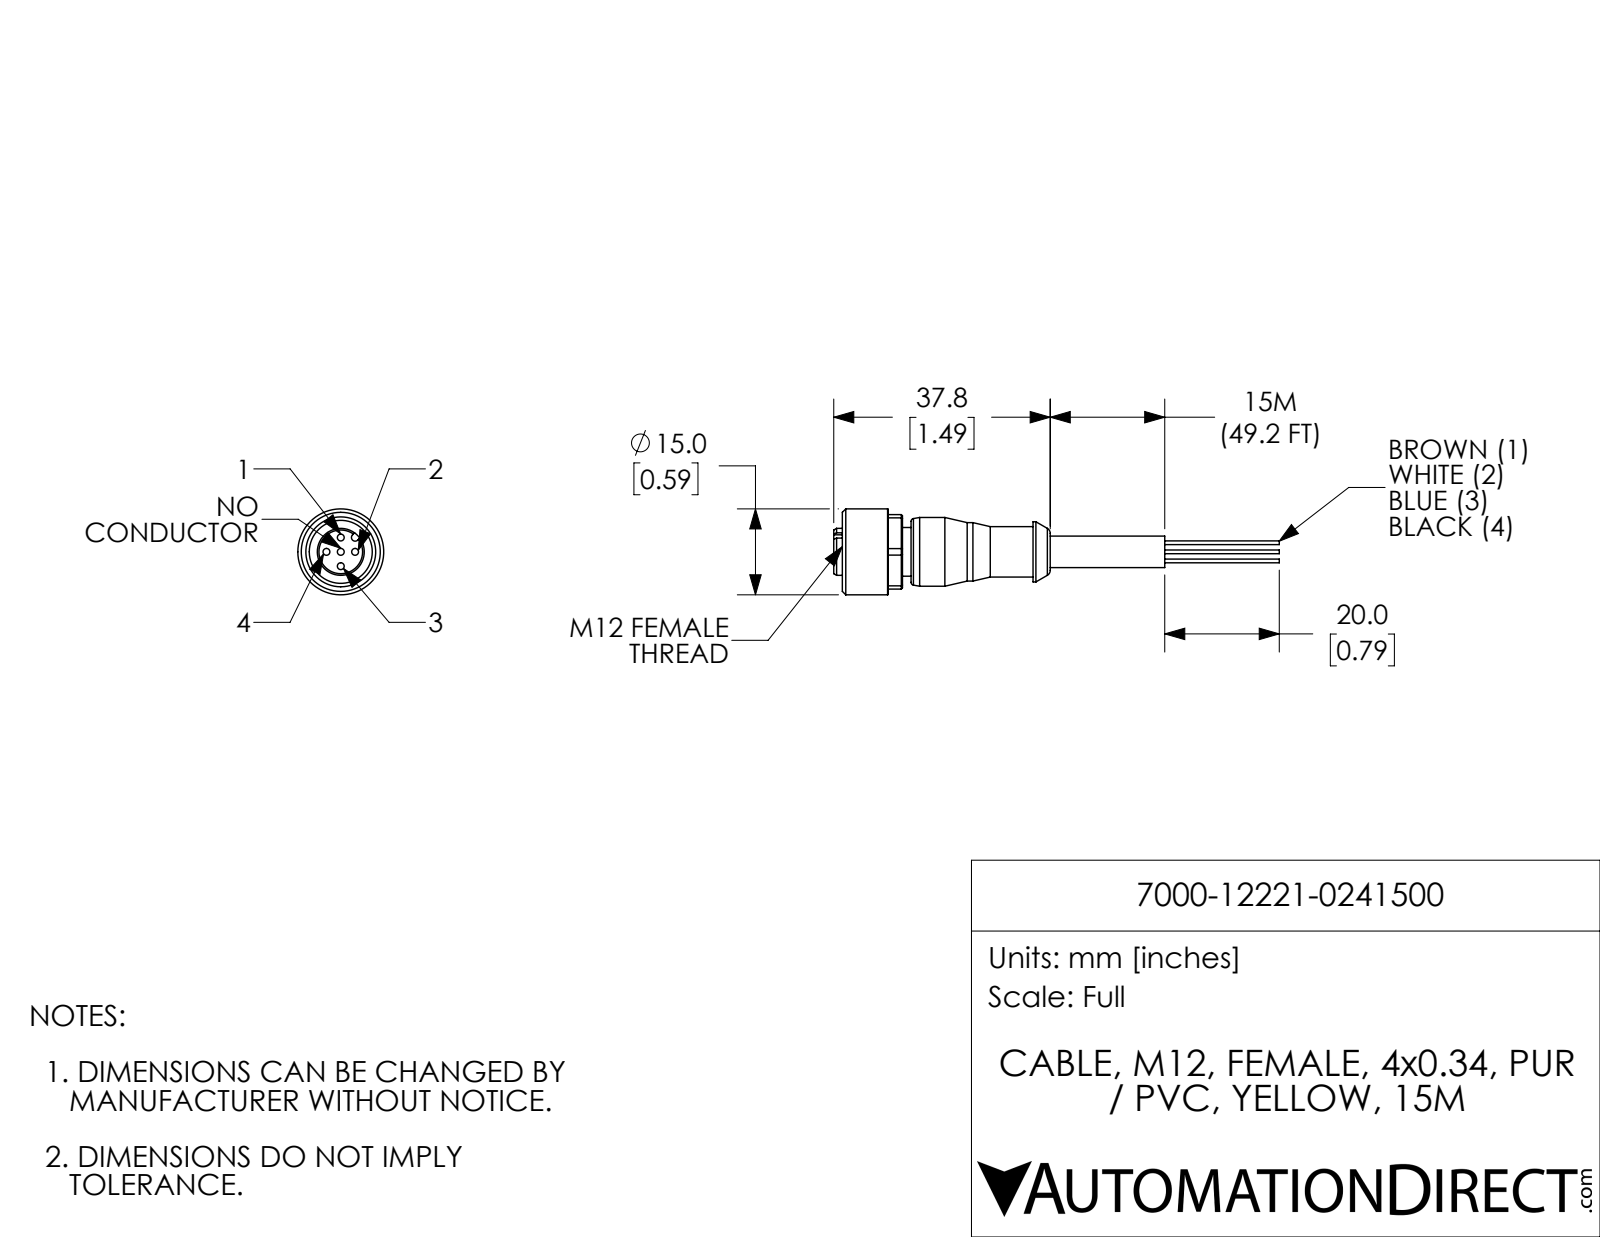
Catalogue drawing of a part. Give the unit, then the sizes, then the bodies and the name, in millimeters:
Units: millimetres
Overall size (bounding box): 77.8 × 15 × 15
Round holes (diameter × count): ⌀1.2 ×5, ⌀11 ×1
Round bosses / shafts (diameter × count): ⌀0.7 ×4, ⌀15 ×1, ⌀12 ×1, ⌀10.5 ×1, ⌀10.2 ×1, ⌀8.8 ×1, ⌀8.5 ×1, ⌀8.2 ×1
Partial cylindrical surfaces — rounded edges, fillets, slot ends (radius × count): R0.7 ×1, R7.2 ×1
Main face-to-face distances: 12, 1.5, 3, 13, 9, 25.8, 7.5, 10.5, 2.5, 13.5
Hole centre spacings: 2.5, 3.5, 5
Volume: 4 050 mm³ · Surface area: 2 830 mm²
Bodies: 1 solid, 103 faces (33 planar, 43 cylindrical, 27 other)
Part name (STEP PRODUCT): 7000-12221-0241500
STEP written by: SolidWorks 2017 (AUTOMOTIVE_DESIGN)
